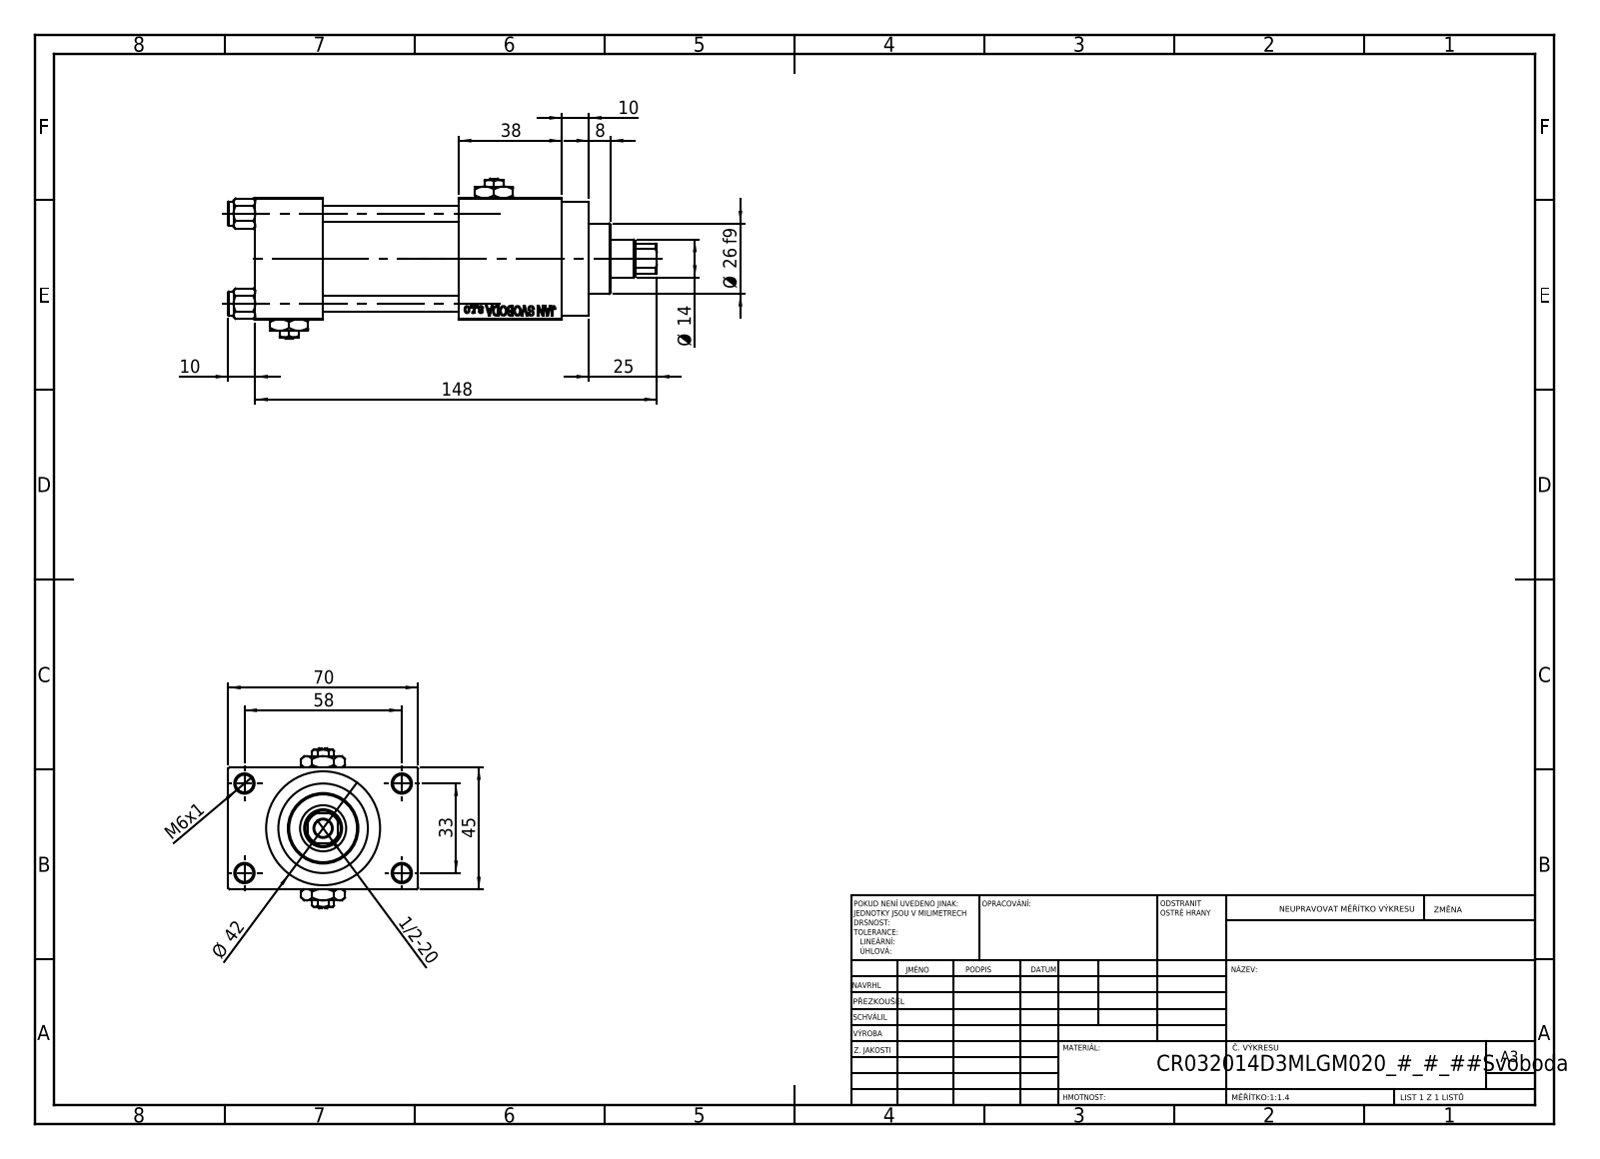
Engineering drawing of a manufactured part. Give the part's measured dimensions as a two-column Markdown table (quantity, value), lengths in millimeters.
| quantity | value |
| --- | --- |
| part name | Zatka_pro_OIL_PORT; V215CR_D_Body; V215_VC_A; V215CR_D_TYCINKA (+2 more) |
| STEP written by | SolidWorks 2019 (CONFIG_CONTROL_DESIGN) |
| units | millimeters |
| bodies | 13 solids, 1187 faces (540 planar, 89 cylindrical, 558 other) |
| overall size | 158 × 70 × 59 |
| volume | 233 596 mm³ |
| surface area | 76 062 mm² |
| round holes (diameter × count) | 6.5 × 5, 6 × 4, 7 × 2, 13.16 × 2, 20 × 2, 14 × 1, 17 × 1, 24 × 1, 32 × 1, 33 × 1 |
| round bosses / shafts (diameter × count) | 9 × 4, 42 × 1, 38 × 1, 26 × 1 |
| partial cylindrical surfaces (radius × count) | 6.5 × 1 |
| main face-to-face distances | 45, 25, 12.5, 57.5, 50, 75, 88, 70, 38, 113 |
| hole center spacings | 12.4, 23.48, 33.2, 33.37, 35.35, 45.6, 56.35, 33 |
